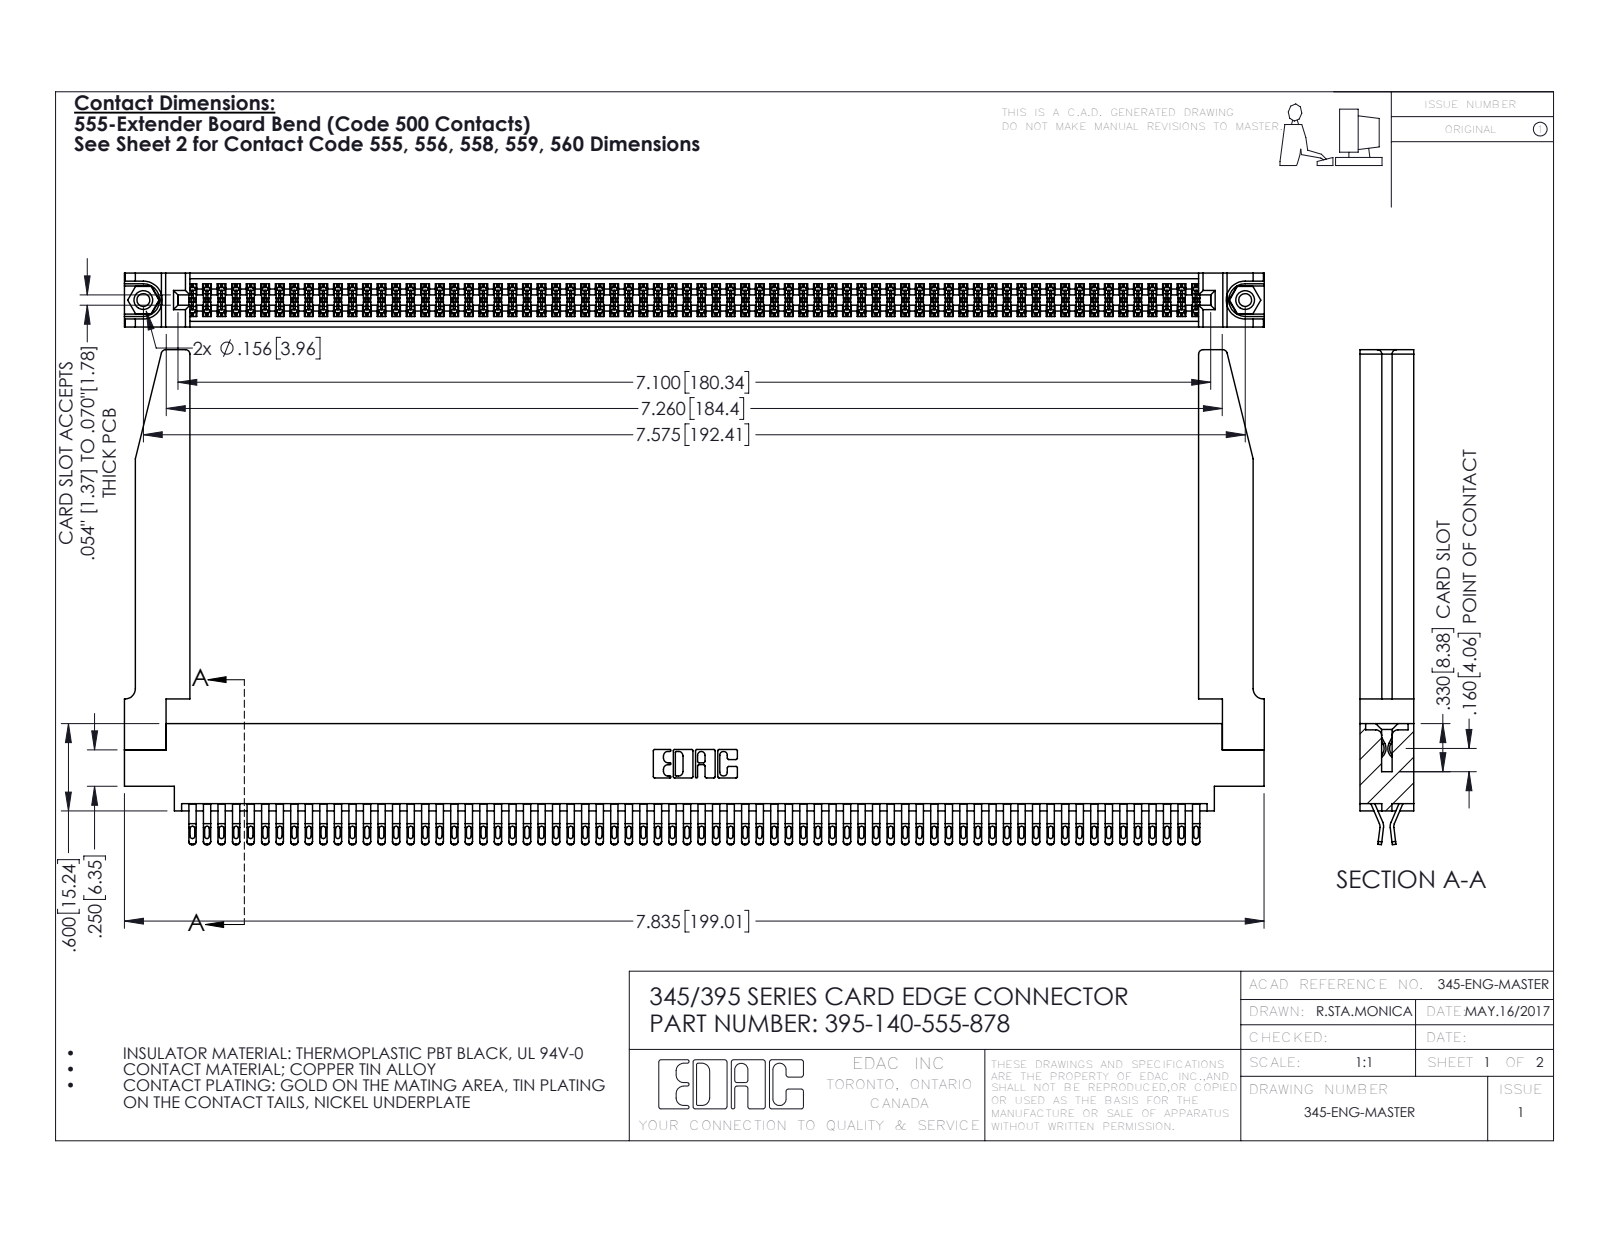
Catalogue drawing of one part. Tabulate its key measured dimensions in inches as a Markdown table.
| quantity | value |
| --- | --- |
| part name | 345-220-078_345-220-078; 345-292-001_555 Tail; 345-250-001_345-250-001-102; 345 Part_0.170 Offset - 0.156 Dia-TH (+1 more) |
| STEP written by | SolidWorks 2016 (CONFIG_CONTROL_DESIGN) |
| units | inches |
| bodies | 145 solids, 8204 faces (4566 planar, 3586 cylindrical, 52 other) |
| overall size | 7.836 × 3.402 × 0.37 |
| volume | 1.688 in³ |
| surface area | 59.42 in² |
| round holes (diameter × count) | 0.089 × 2, 0.125 × 2, 0.156 × 2, 0.064 × 1 |
| round bosses / shafts (diameter × count) | 0.155 × 2 |
| partial cylindrical surfaces (radius × count) | 0.016 × 350, 0.02 × 280, 0.006 × 210, 0.01 × 22, 0.03 × 8, 0.007 × 6, 0.031 × 6, 0.026 × 3 |
| main face-to-face distances | 0.072, 0.37, 0.298, 0.025, 0.098, 0.272, 0.2, 0.225, 0.175, 0.149 |
| hole center spacings | 0.27, 7.339, 7.575 |
